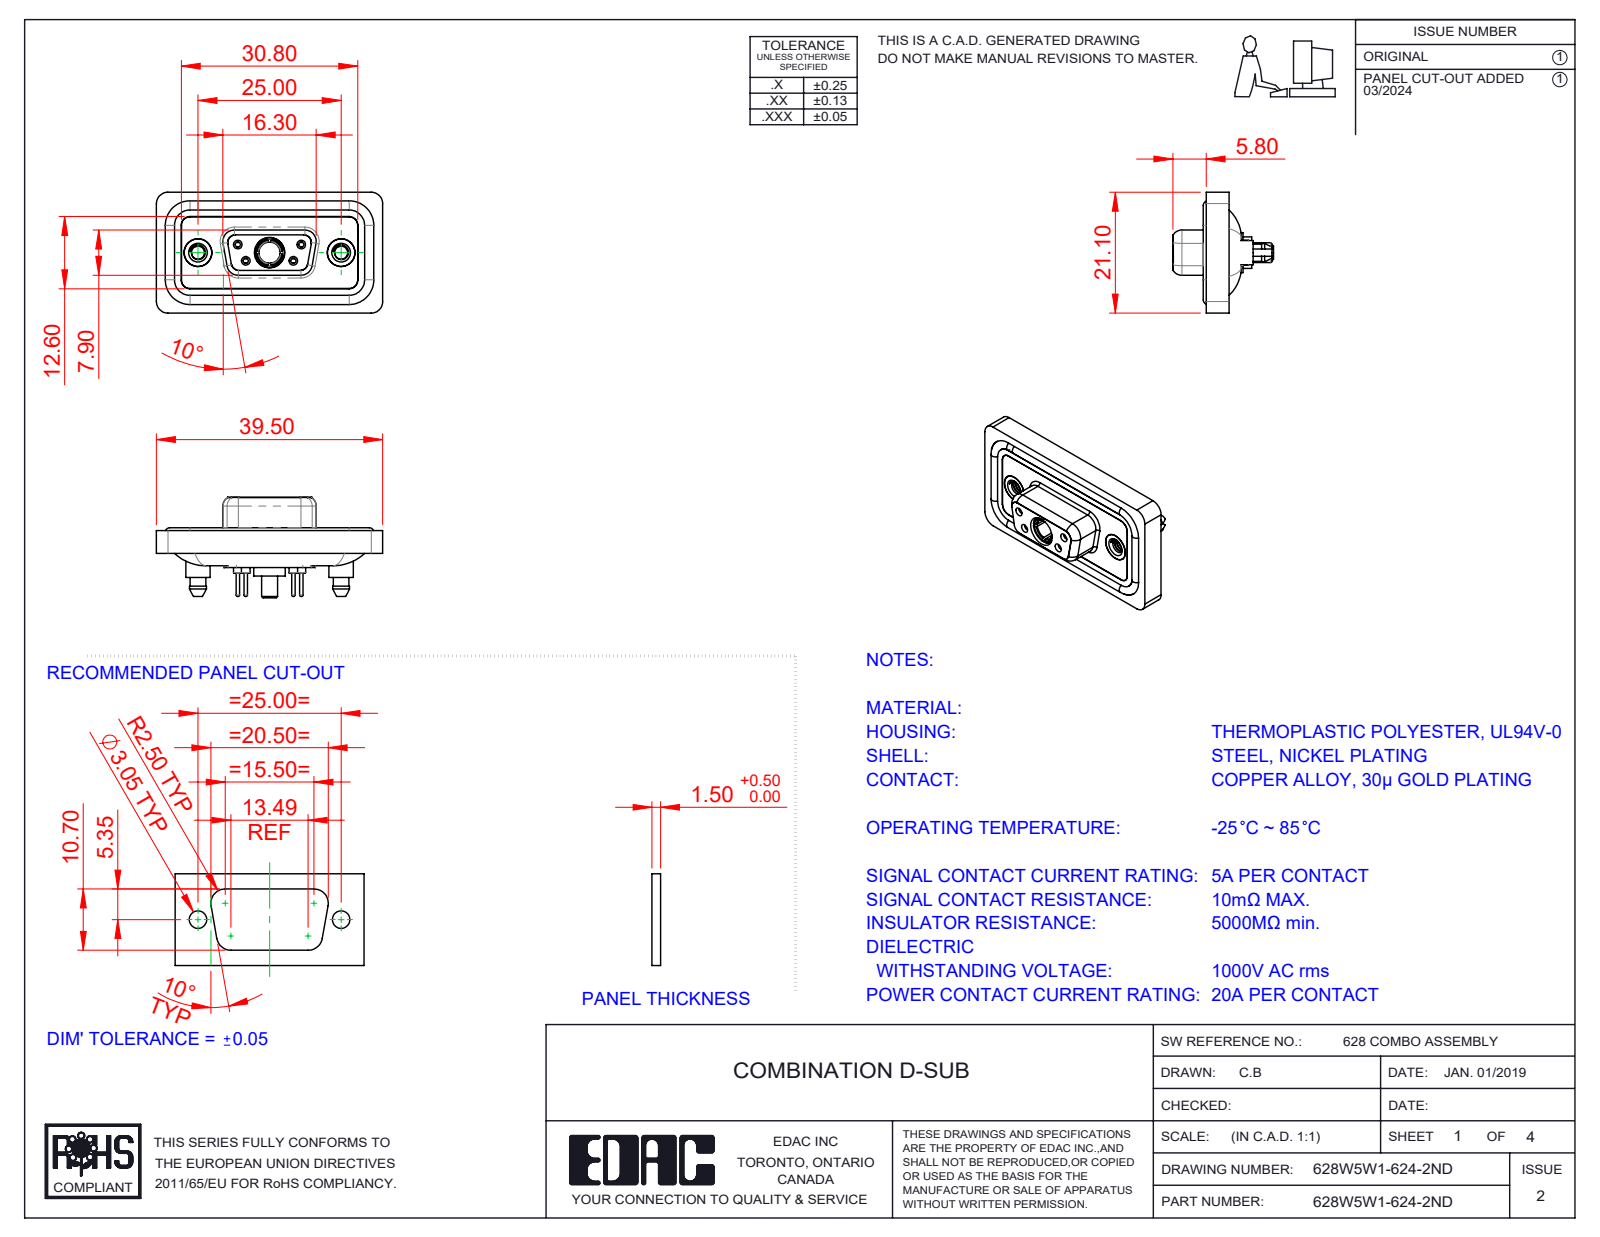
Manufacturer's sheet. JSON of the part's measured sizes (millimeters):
{"part_name": "628Combo Shell Front_09 Contacts; Power Socket_20A S; 628Combo Waterproof Housing_09 Contacts; 628Combo Threaded Boardlock_D (+5 more)", "step_written_by": "SolidWorks 2023 (CONFIG_CONTROL_DESIGN)", "units": "millimeters", "bodies": {"solids": 13, "faces": 746, "planar": 210, "cylindrical": 335, "other": 201}, "overall_size": [39.5, 21.1, 17.55], "volume_mm3": 4902, "surface_area_mm2": 7975, "round_holes": [[0.9, 4], [1.1, 4], [1.5, 4], [2, 4], [4.85, 3], [1.6, 2], [1.7, 2], [2.26, 2], [4, 2], [4.05, 2], [5, 2], [3.7, 1]], "round_bosses_or_shafts": [[1.6, 6], [2.2, 4], [0.6, 4], [5.4, 2], [4.95, 2], [4.8, 2], [4.25, 2], [5.5, 1]], "partial_cylinders_radius": [[1.5, 24], [2, 18], [1.6, 10], [1.35, 8], [0.25, 4], [0.5, 4], [0.6, 4], [0.65, 4]], "face_to_face_distances": [0.4, 2.9, 1.1, 1.8, 1.6, 0.5, 5.65, 7.45, 5.35, 3.6], "hole_center_spacings": [3.16, 5.72, 7.1, 12.5, 18.1, 4.39, 4.4, 8.31]}
